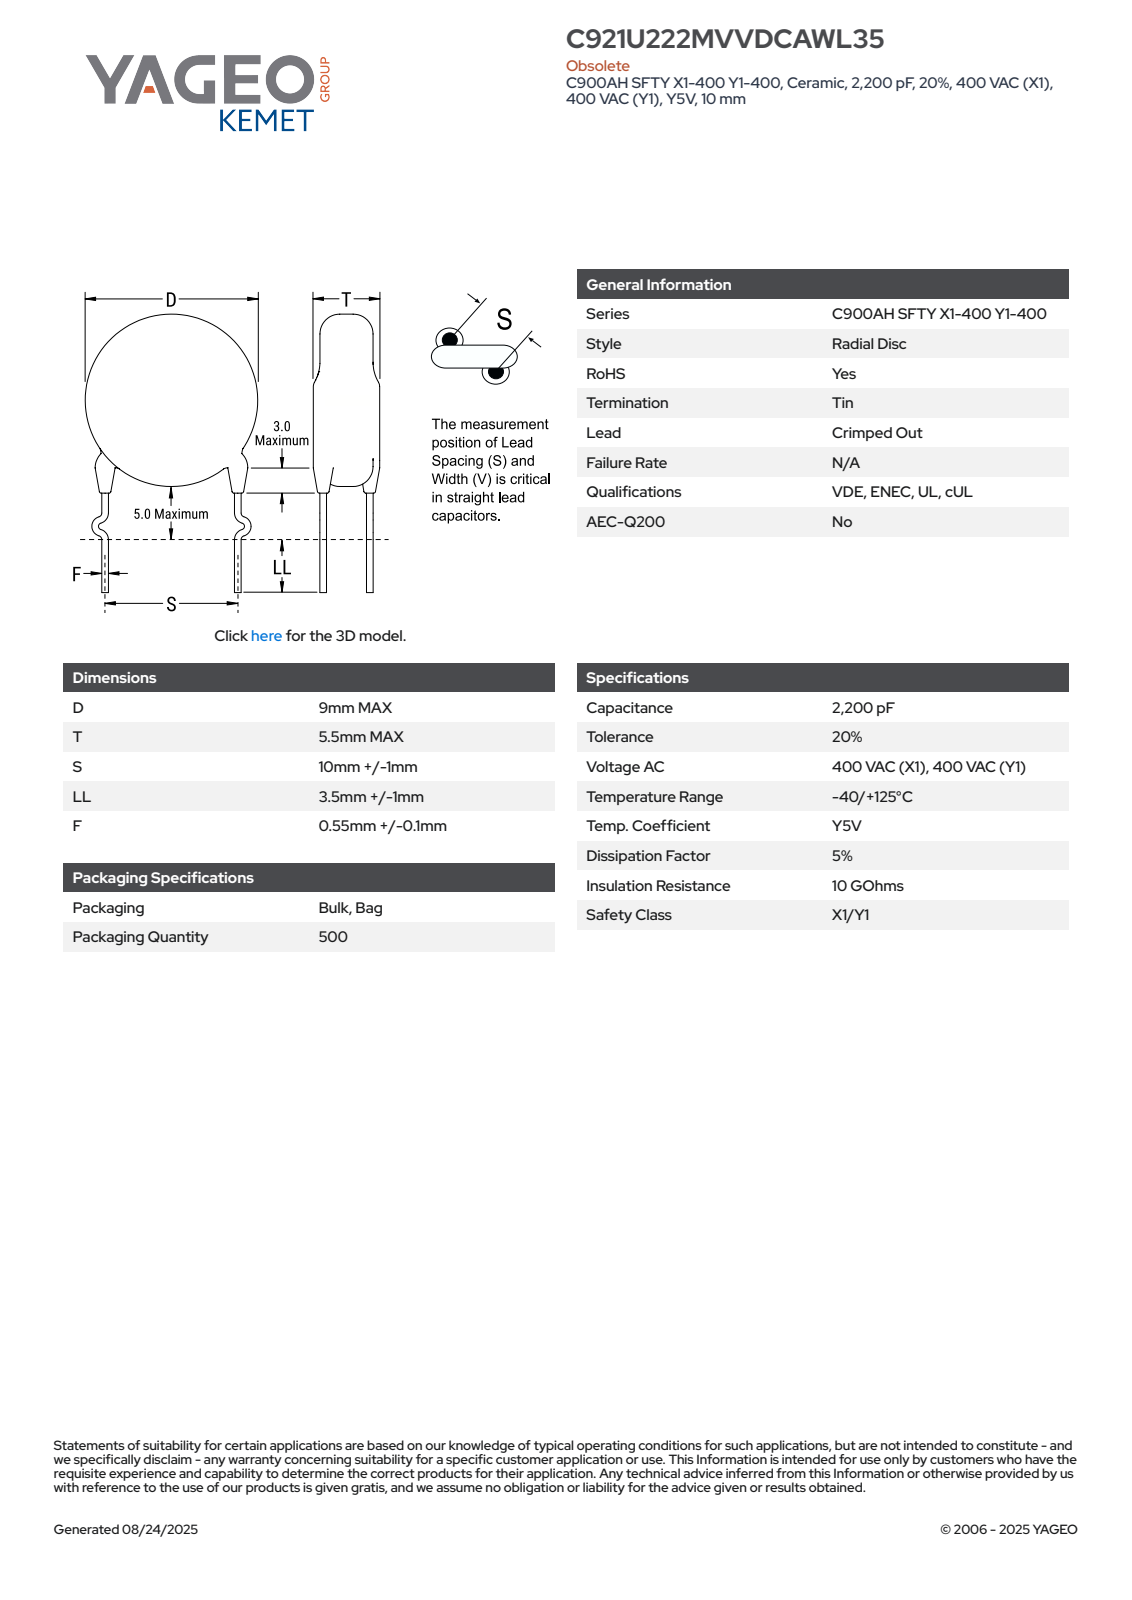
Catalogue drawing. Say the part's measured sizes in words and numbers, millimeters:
The part is named "CCD_KCOC900_D9T5.5S10LL4.5F0.55". Its 3-D file was written by "SolidWorks 2014 (AUTOMOTIVE_DESIGN)". It is 4 solids with 93 faces: 63 planar, 10 cylindrical and 20 other. Overall it measures 18.5 by 14.29 by 6.24 millimeters. Its volume is 353 cubic millimeters and its surface area 336 square millimeters. Round bosses or shafts: 2 of diameter 1.2, 1 of diameter 9. Partial cylindrical surfaces (rounded edges, fillets, slot ends): 2 of radius 0.6. The main face-to-face distances are 5.5, 0.94, 4.98, 4.04, 0.76, 3.82, 0.58, 4.07, 2.77, 2.88.
